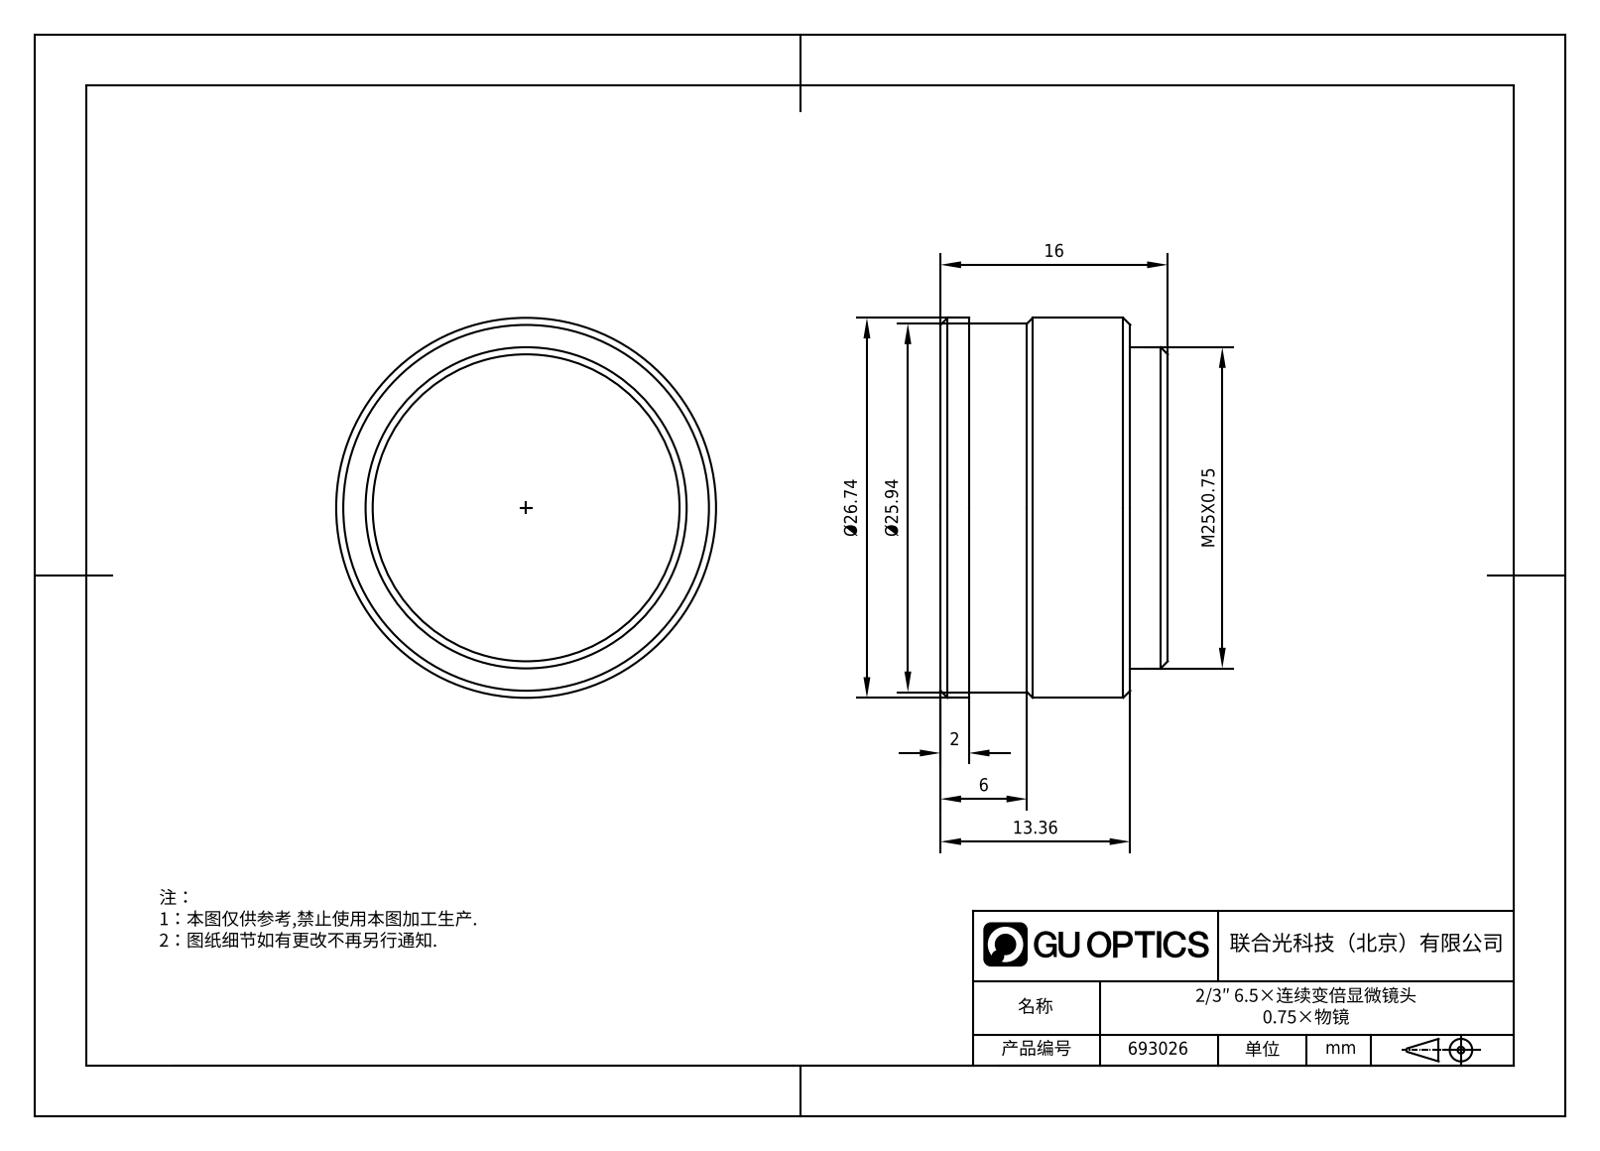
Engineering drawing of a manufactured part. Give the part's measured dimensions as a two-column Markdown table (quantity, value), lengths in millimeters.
| quantity | value |
| --- | --- |
| part name | 66175 |
| STEP written by | SolidWorks 2015 (CONFIG_CONTROL_DESIGN) |
| units | millimeters |
| bodies | 1 solid, 20 faces (4 planar, 8 cylindrical, 8 other) |
| overall size | 26.74 × 26.74 × 16 |
| volume | 8 390 mm³ |
| surface area | 2 398 mm² |
| round bosses / shafts (diameter × count) | 26.74 × 1, 25.94 × 1, 22.6 × 1 |
| main face-to-face distances | 16, 13.36, 2.64, 2, 11.36, 14 |
